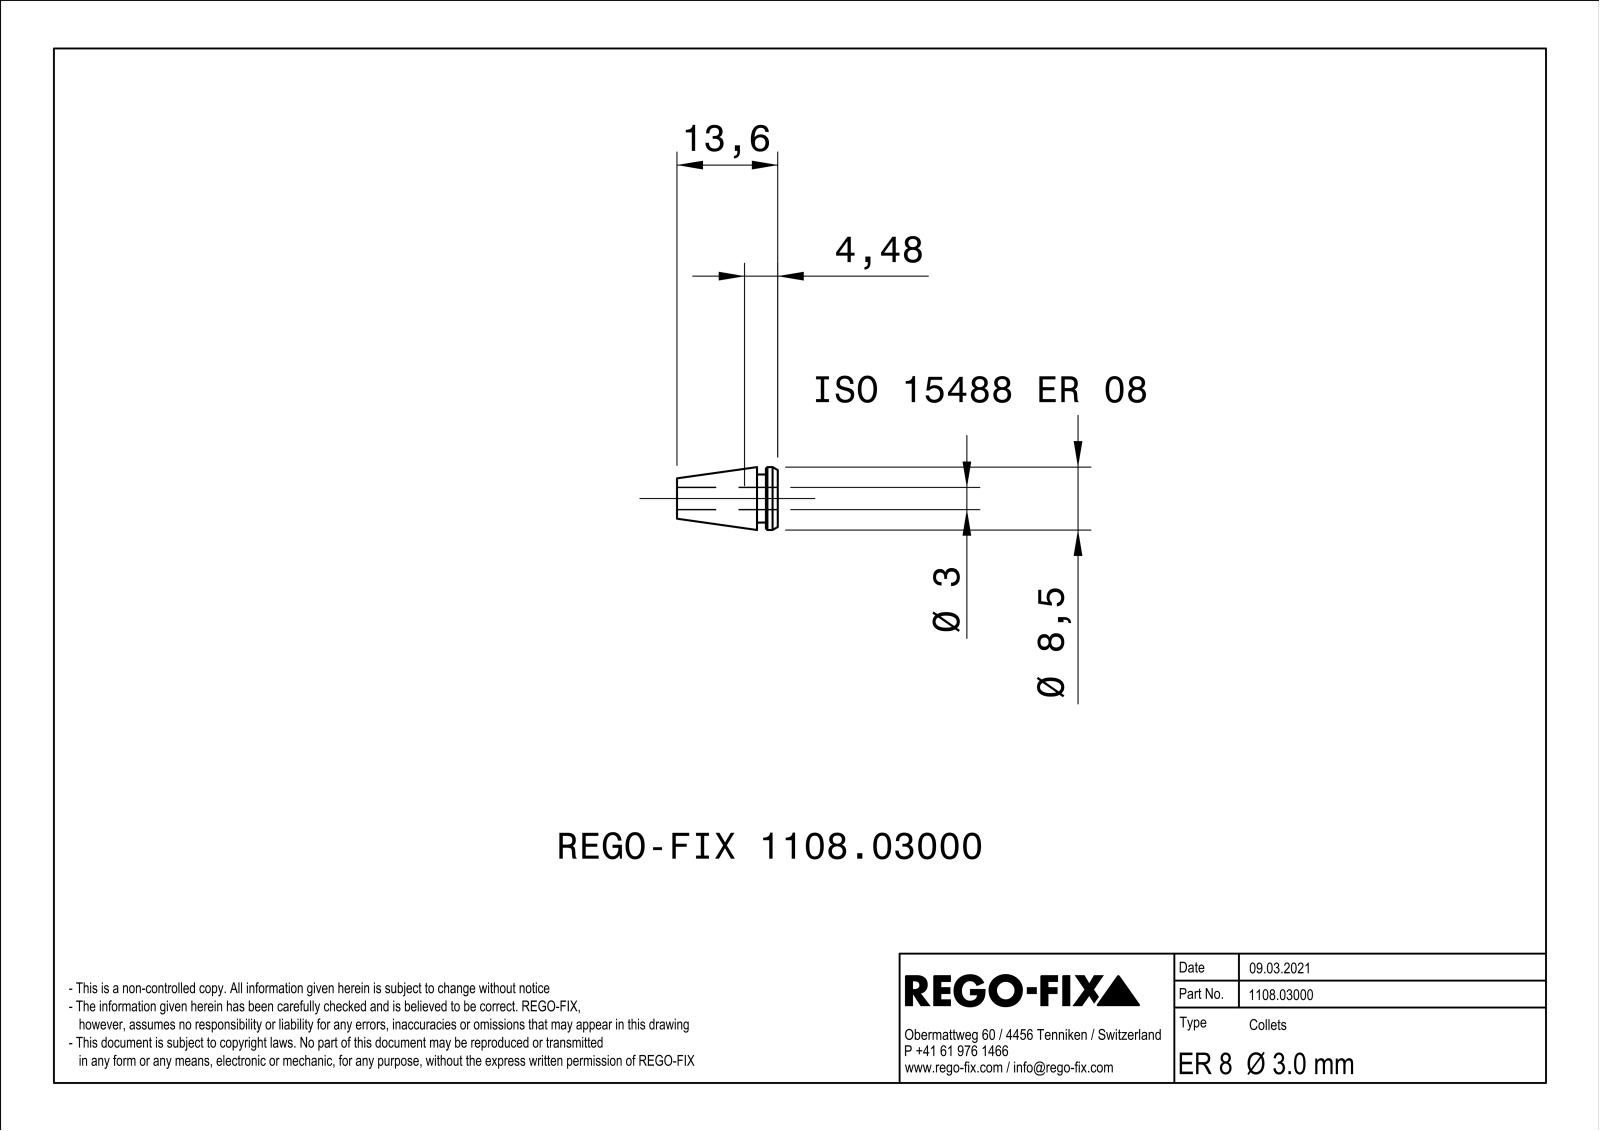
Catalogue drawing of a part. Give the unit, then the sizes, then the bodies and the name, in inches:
Units: inches
Overall size (bounding box): 0.535 × 0.334 × 0.334
Round holes (diameter × count): ⌀0.118 ×1
Round bosses / shafts (diameter × count): ⌀0.335 ×1, ⌀0.256 ×1
Partial cylindrical surfaces — rounded edges, fillets, slot ends (radius × count): R0.787 ×12
Main face-to-face distances: 0.016, 0.11, 0.063, 0.047, 0.535, 0.472, 0.425
Volume: 0.021 in³ · Surface area: 1.53 in²
Bodies: 1 solid, 211 faces (90 planar, 43 cylindrical, 78 other)
Part name (STEP PRODUCT): NOCUT
STEP written by: SIEMENS PLM Software Solid Edge ST10 (AUTOMOTIVE_DESIGN)
